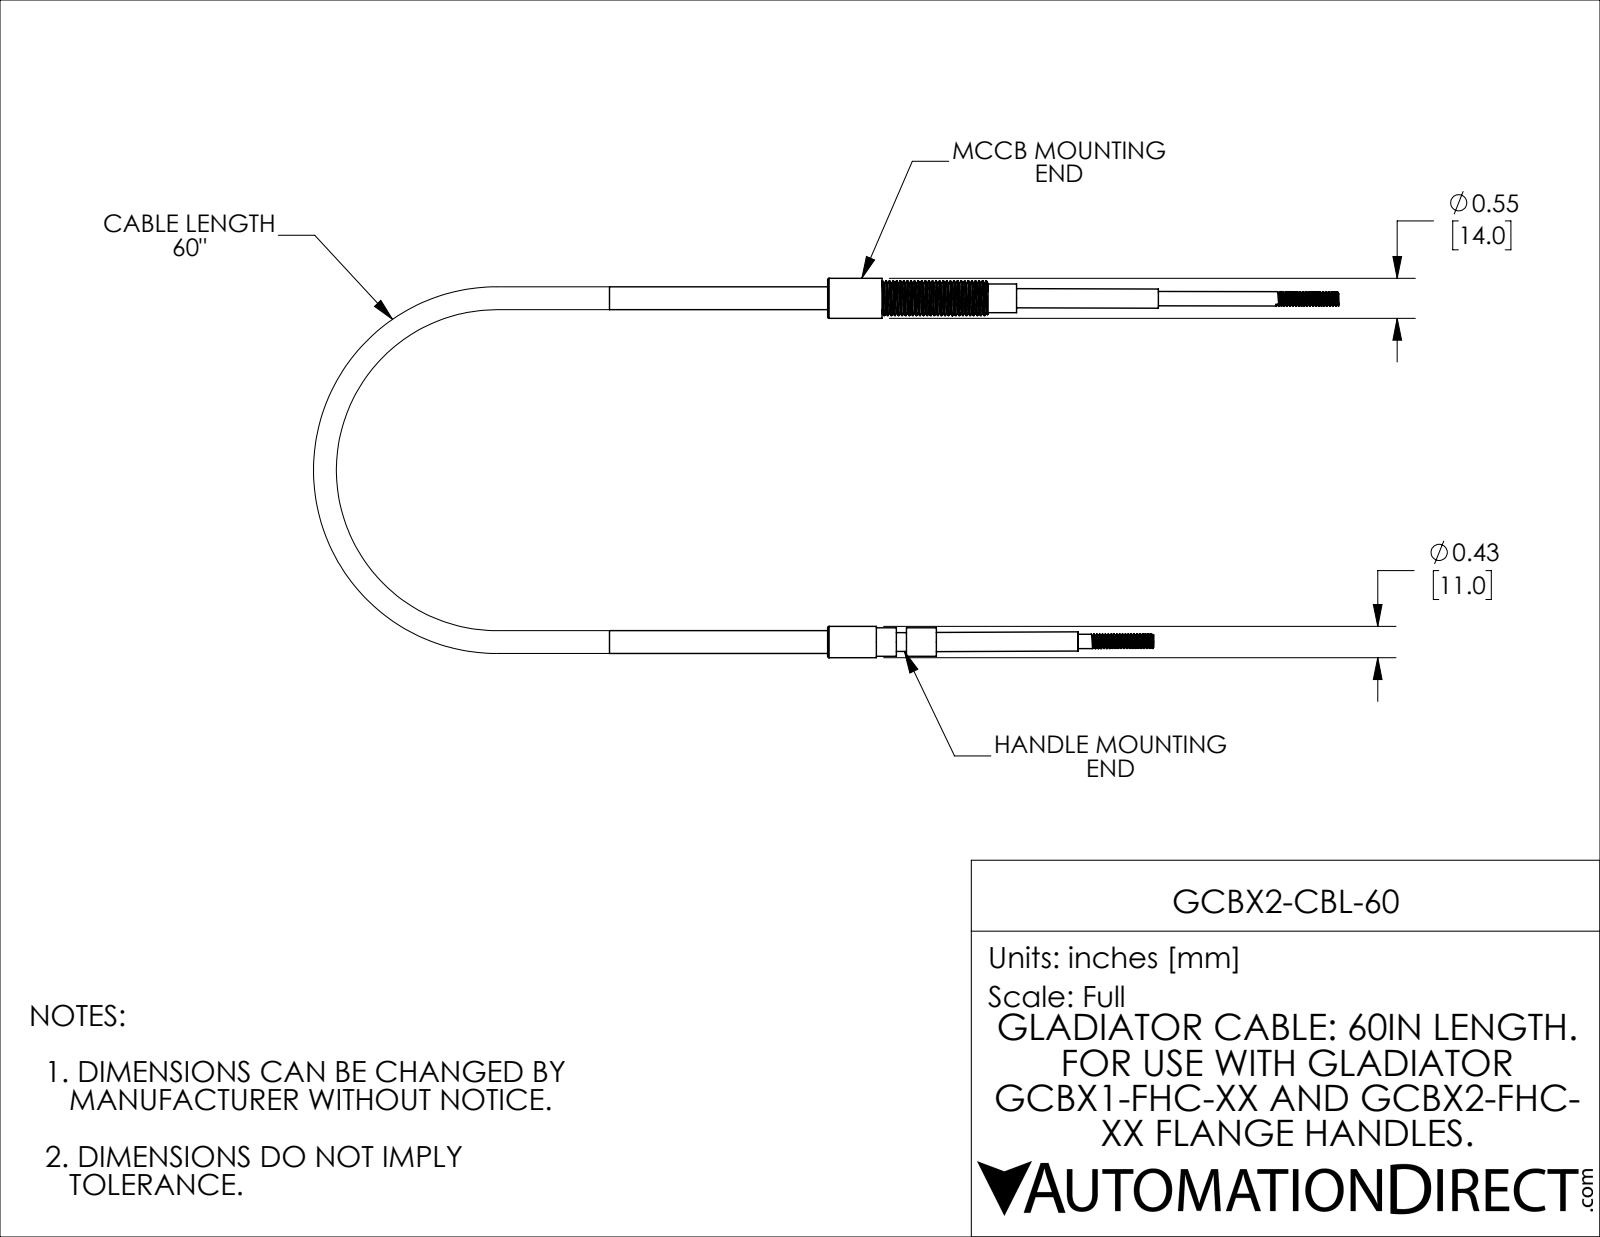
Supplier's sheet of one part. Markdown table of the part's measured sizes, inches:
| quantity | value |
| --- | --- |
| part name | GCBX2-CBL-60; GCBX2-CBL-60_2; GCBX2-CBL-60_1 |
| STEP written by | SolidWorks 2021 (CONFIG_CONTROL_DESIGN) |
| units | inches |
| bodies | 8 solids, 273 faces (30 planar, 187 cylindrical, 56 other) |
| overall size | 10.028 × 5.217 × 1.358 |
| volume | 1.36 in³ |
| surface area | 29.56 in² |
| round holes (diameter × count) | 0.201 × 2, 0.118 × 1, 0.245 × 1, 0.256 × 1, 0.315 × 1 |
| round bosses / shafts (diameter × count) | 0.394 × 2, 0.287 × 2, 0.264 × 2, 0.197 × 2, 0.551 × 1, 0.472 × 1, 0.433 × 1, 0.315 × 1 |
| main face-to-face distances | 1.181, 3, 1.819, 2.598, 3.78, 5.598, 0.748, 1.85, 1.929, 0.413 |
| hole center spacings | 4.803 |
